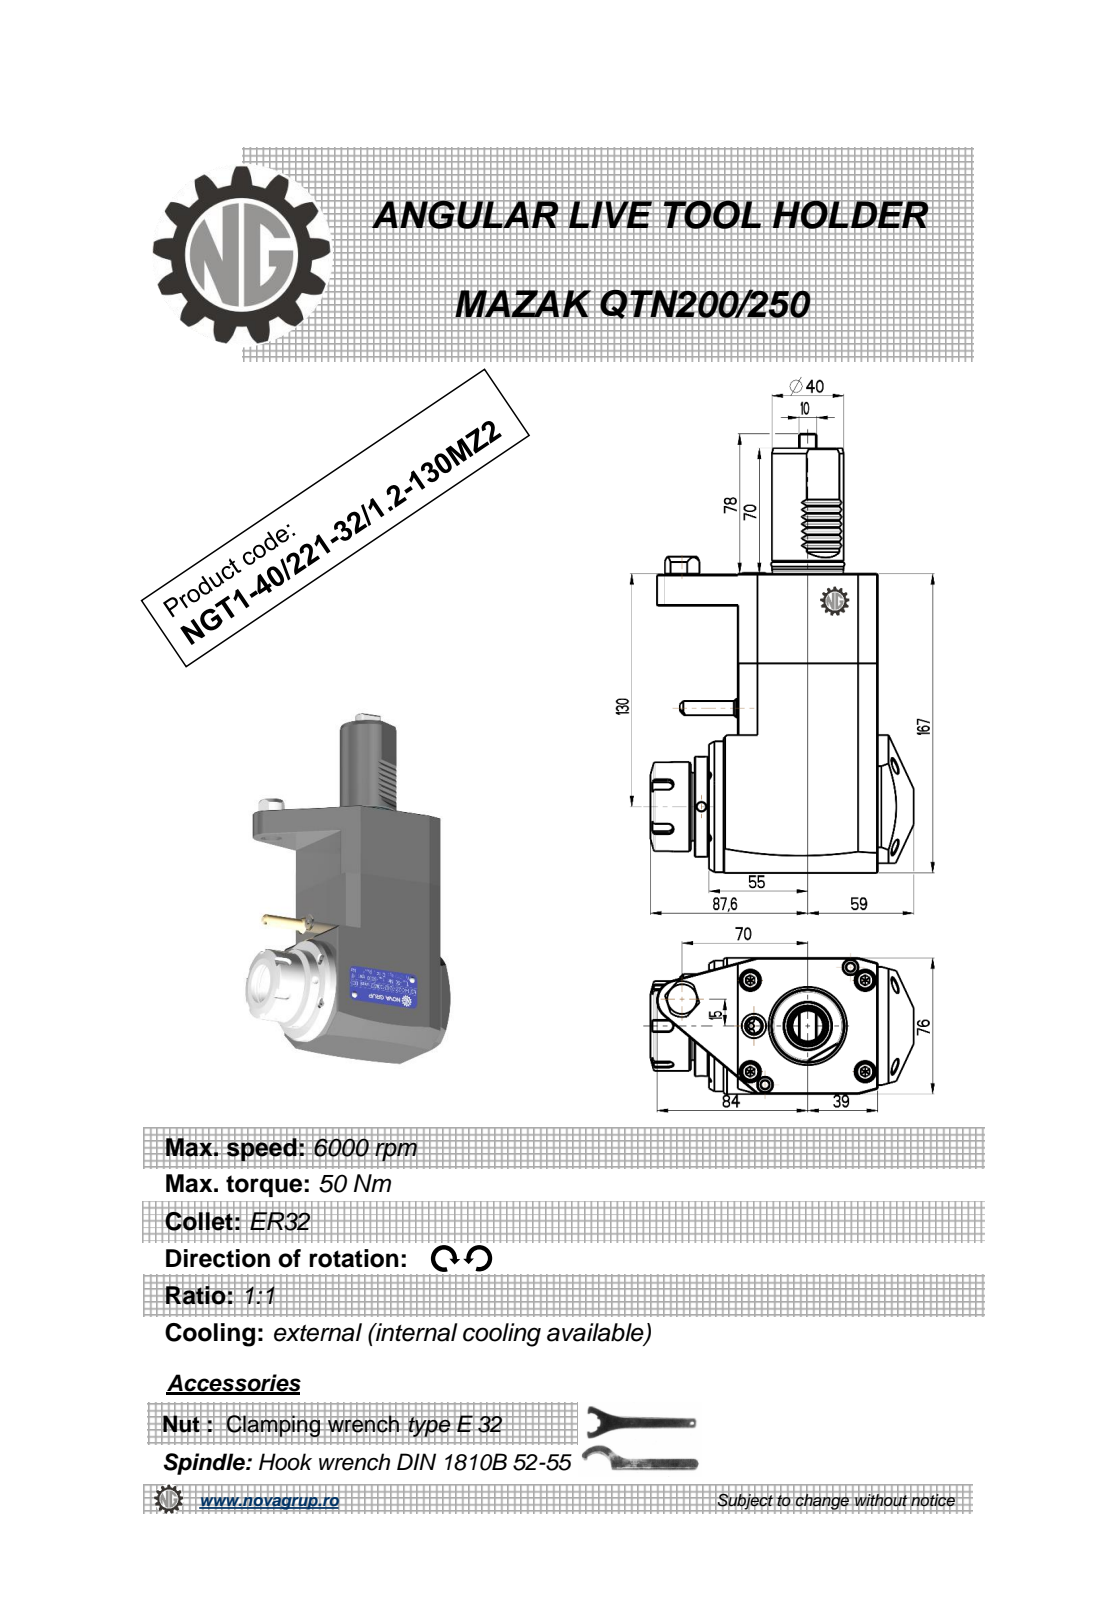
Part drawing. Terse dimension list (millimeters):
name: NGT1_40_221_32_1_2_130MZ2
written by: PRO/ENGINEER BY PARAMETRIC TECHNOLOGY CORPORATION, 2010280 (CONFIG_CONTROL_DESIGN)
unit: mm
bodies: 1 solid, 2436 faces (2271 planar, 74 cylindrical, 91 other)
size: 245 × 146.6 × 77.6
volume: 1 284 000 mm³; area: 91 983 mm²
holes: 3× ⌀5, 1× ⌀3, 1× ⌀8, 1× ⌀27
bosses: 1× ⌀73, 1× ⌀56, 1× ⌀50, 1× ⌀43, 1× ⌀40, 1× ⌀39.4, 1× ⌀36.2, 1× ⌀10
rounds: 7× R0.3, 6× R0.2, 5× R3, 2× R0.8, 2× R300, 1× R9, 1× R10, 1× R11.35
face distances: 76, 78, 167, 8, 16, 94, 18, 87.92, 149, 86
hole spacings: 29.25, 60.42
